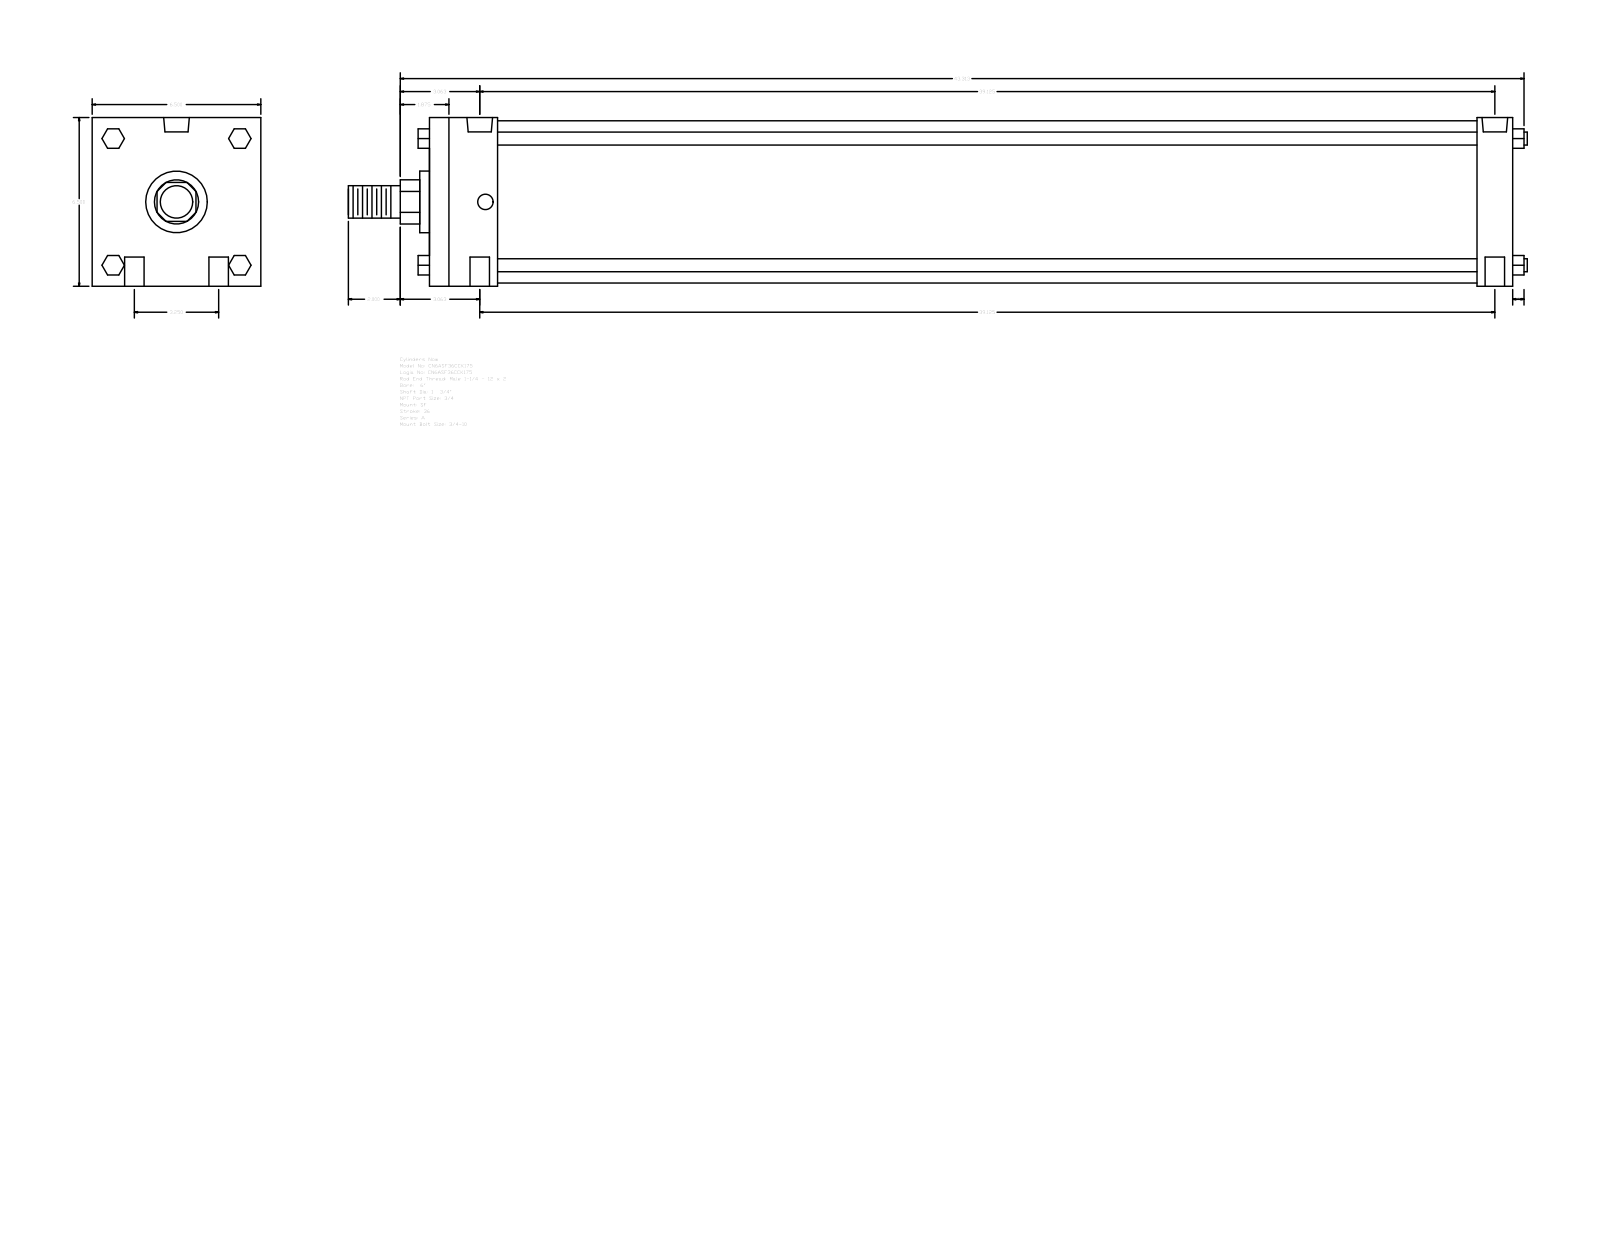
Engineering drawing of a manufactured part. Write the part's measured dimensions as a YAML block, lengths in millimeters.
part_name: "A_SF__0600_1.75"
step_written_by: "GSSL Pune (CONFIG_CONTROL_DESIGN)"
units: millimeters
bodies: {solids: 0, faces: 124, planar: 94, cylindrical: 30, other: 0}
overall_size: [1154.11, 165.1, 165.1]
round_holes:
  - {diameter: 19.05, count: 4}
  - {diameter: 15.08, count: 2}
  - {diameter: 25.12, count: 2}
round_bosses_or_shafts:
  - {diameter: 12.7, count: 4}
  - {diameter: 158.75, count: 1}
  - {diameter: 60.33, count: 1}
  - {diameter: 44.45, count: 1}
  - {diameter: 31.75, count: 1}
partial_cylinders:
  - {radius: 21.63, count: 1}
face_to_face_distances: [165.1, 1060.46, 66.68, 1025.53, 34.93, 958.85, 993.78, 19.05, 61.97, 107.34]
hole_center_spacings: [41.27, 994.63, 993.77, 82.54, 997.19, 982.65]
